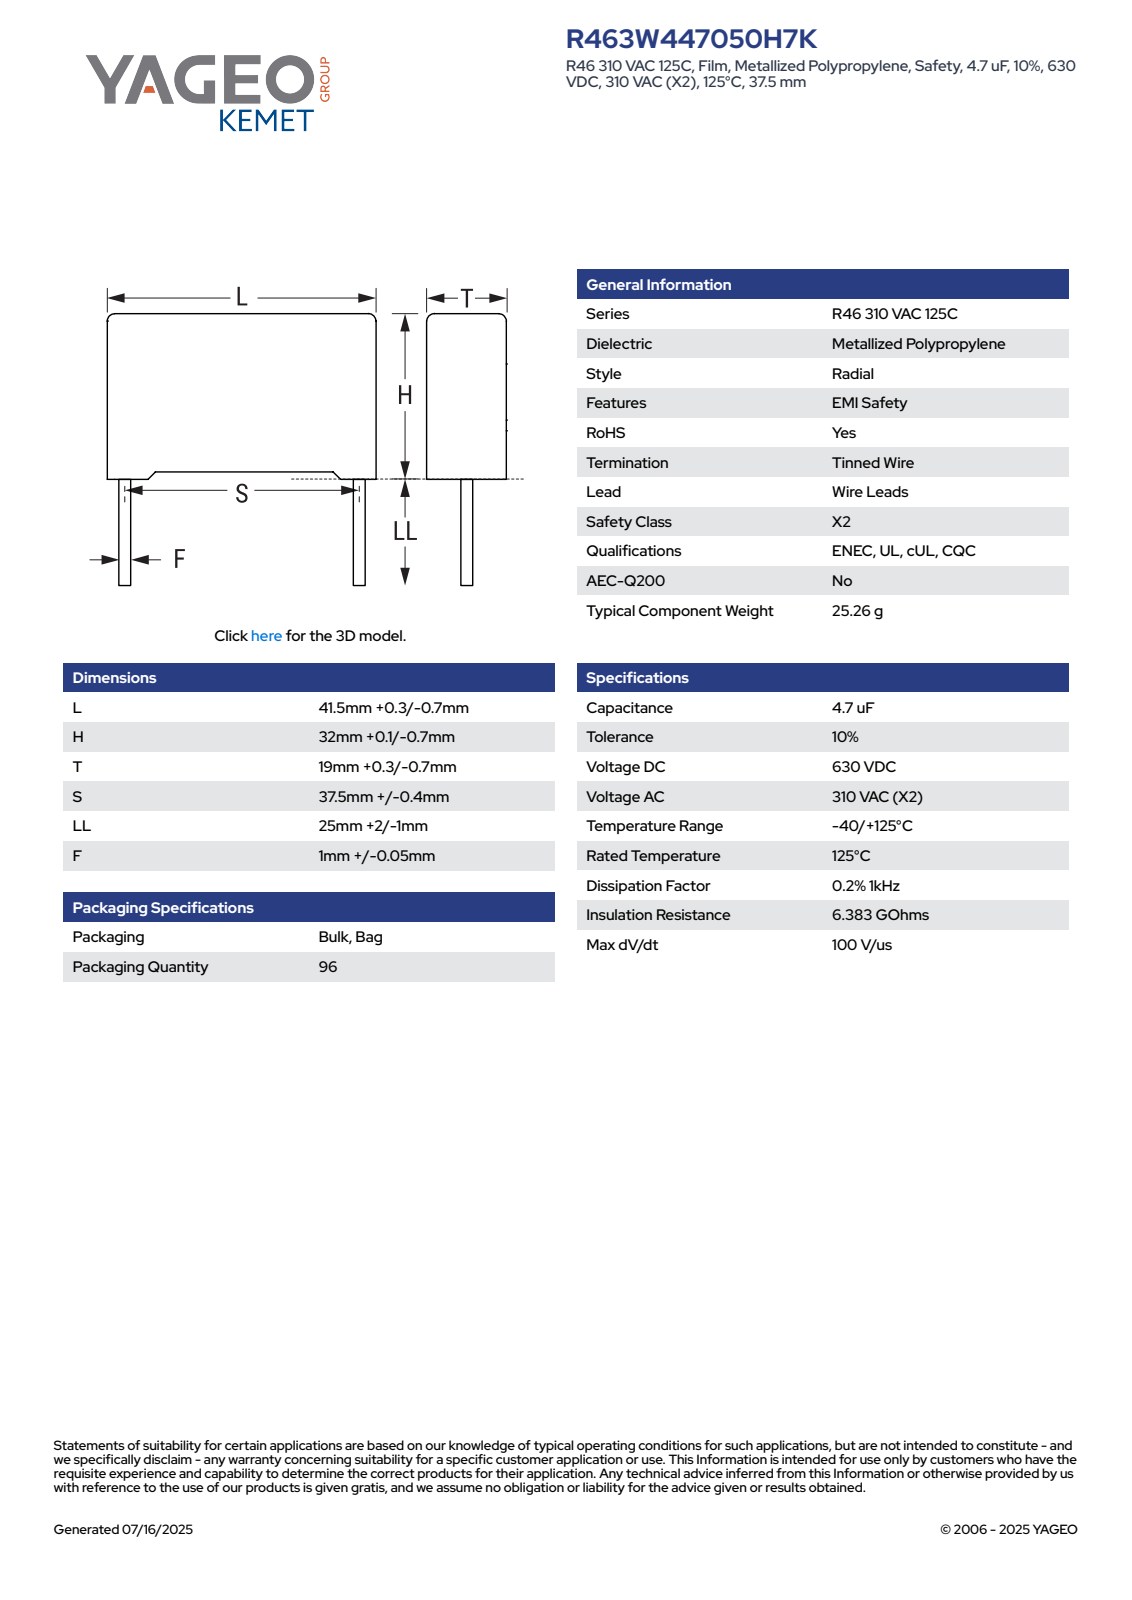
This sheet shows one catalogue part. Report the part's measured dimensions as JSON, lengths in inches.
{"part_name": "CFR_RB2_41.5X32X19_L41.8H32.1T19.3S37.5LL27F1.05", "step_written_by": "SolidWorks 2021 (AUTOMOTIVE_DESIGN)", "units": "inches", "bodies": {"solids": 4, "faces": 85, "planar": 77, "cylindrical": 8, "other": 0}, "overall_size": [2.327, 1.646, 0.76], "volume_in3": 1.535, "surface_area_in2": 8.975, "round_bosses_or_shafts": [[0.041, 2]], "partial_cylinders_radius": [[0.02, 4]], "face_to_face_distances": [0.76, 1.22, 1.646, 0.014, 1.234, 0.03, 0.044, 1.264, 0.055, 0.76]}
